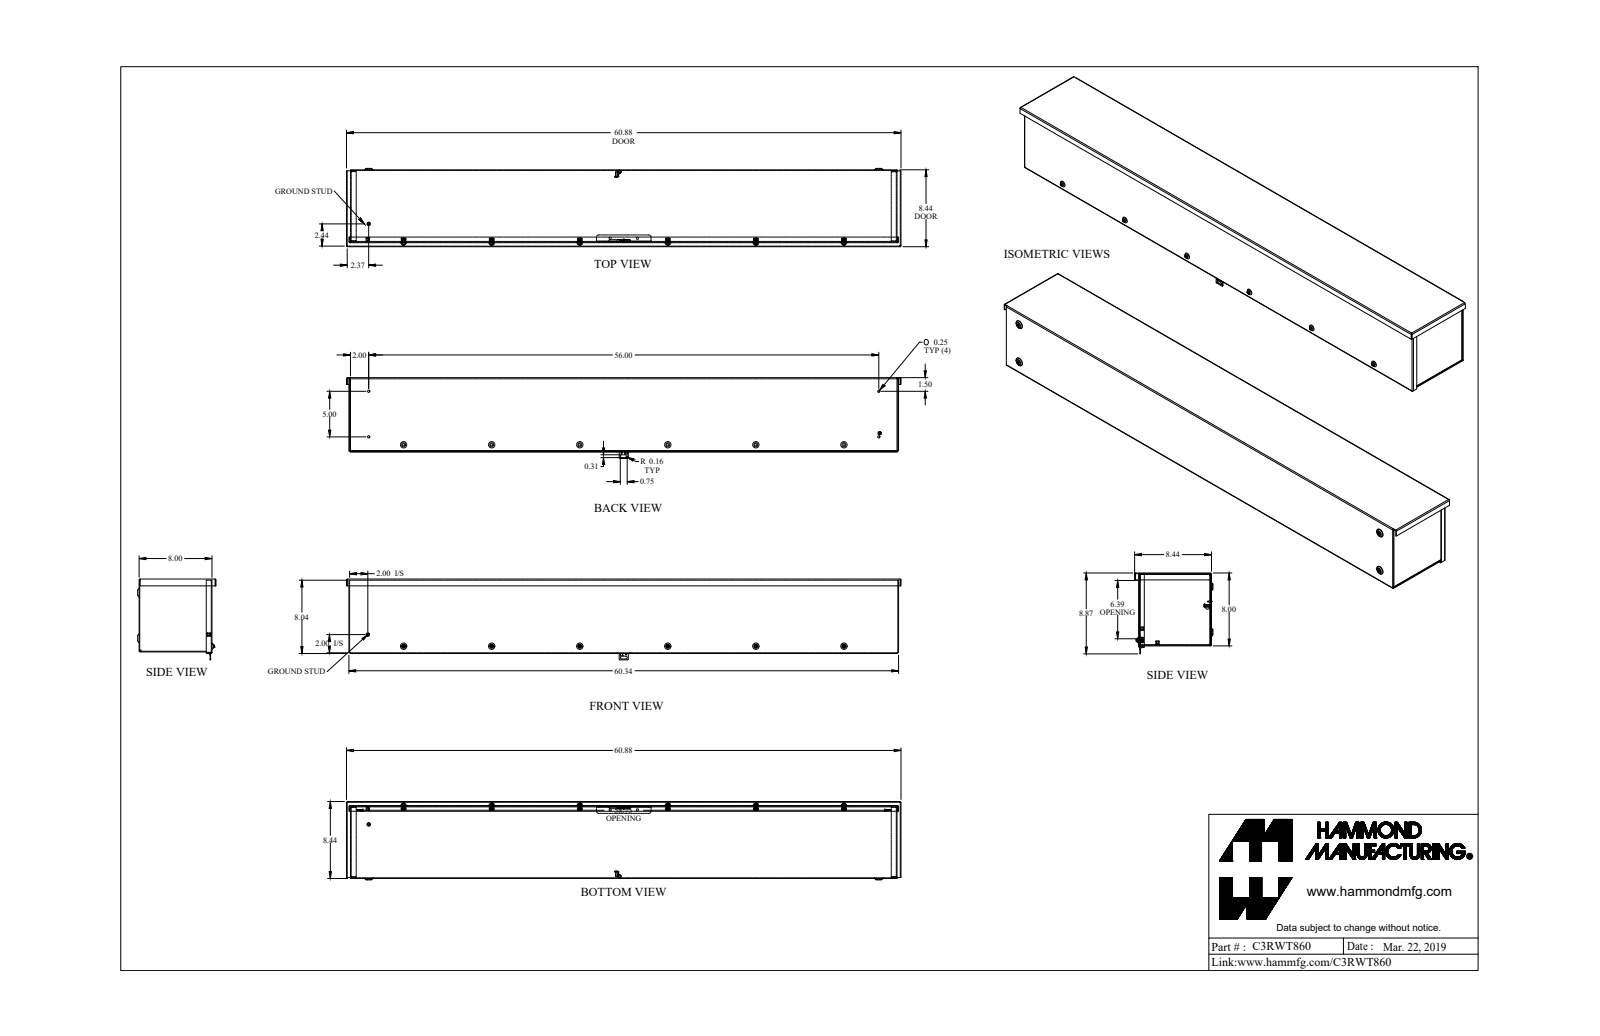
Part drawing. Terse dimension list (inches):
name: C3RWT860_Default
written by: SolidWorks 2019 (CONFIG_CONTROL_DESIGN)
unit: in
bodies: 31 solids, 1127 faces (628 planar, 351 cylindrical, 148 other)
size: 60.875 × 8.871 × 8.594
volume: 162 in³; area: 4 541 in²
holes: 8× ⌀0.156, 6× ⌀0.214, 6× ⌀0.23, 6× ⌀0.25, 2× ⌀0.203, 1× ⌀0.125, 1× ⌀0.137, 1× ⌀0.2, 1× ⌀0.215
bosses: 7× ⌀0.19, 6× ⌀0.148, 2× ⌀0.375, 1× ⌀0.5, 1× ⌀0.367, 1× ⌀0.21, 1× ⌀0.152, 1× ⌀0.125
rounds: 24× R0.08, 24× R0.108, 18× R0.036, 18× R0.108, 14× R0.125, 12× R0.022, 6× R0.171, 6× R0.206
face distances: 0.072, 7.928, 7.856, 8, 59.928, 8.366, 0.51, 0.438, 0.172, 0.144
hole spacings: 9.669, 29.006, 19.337, 19.338, 3.778, 4.837, 9.669, 11.856
